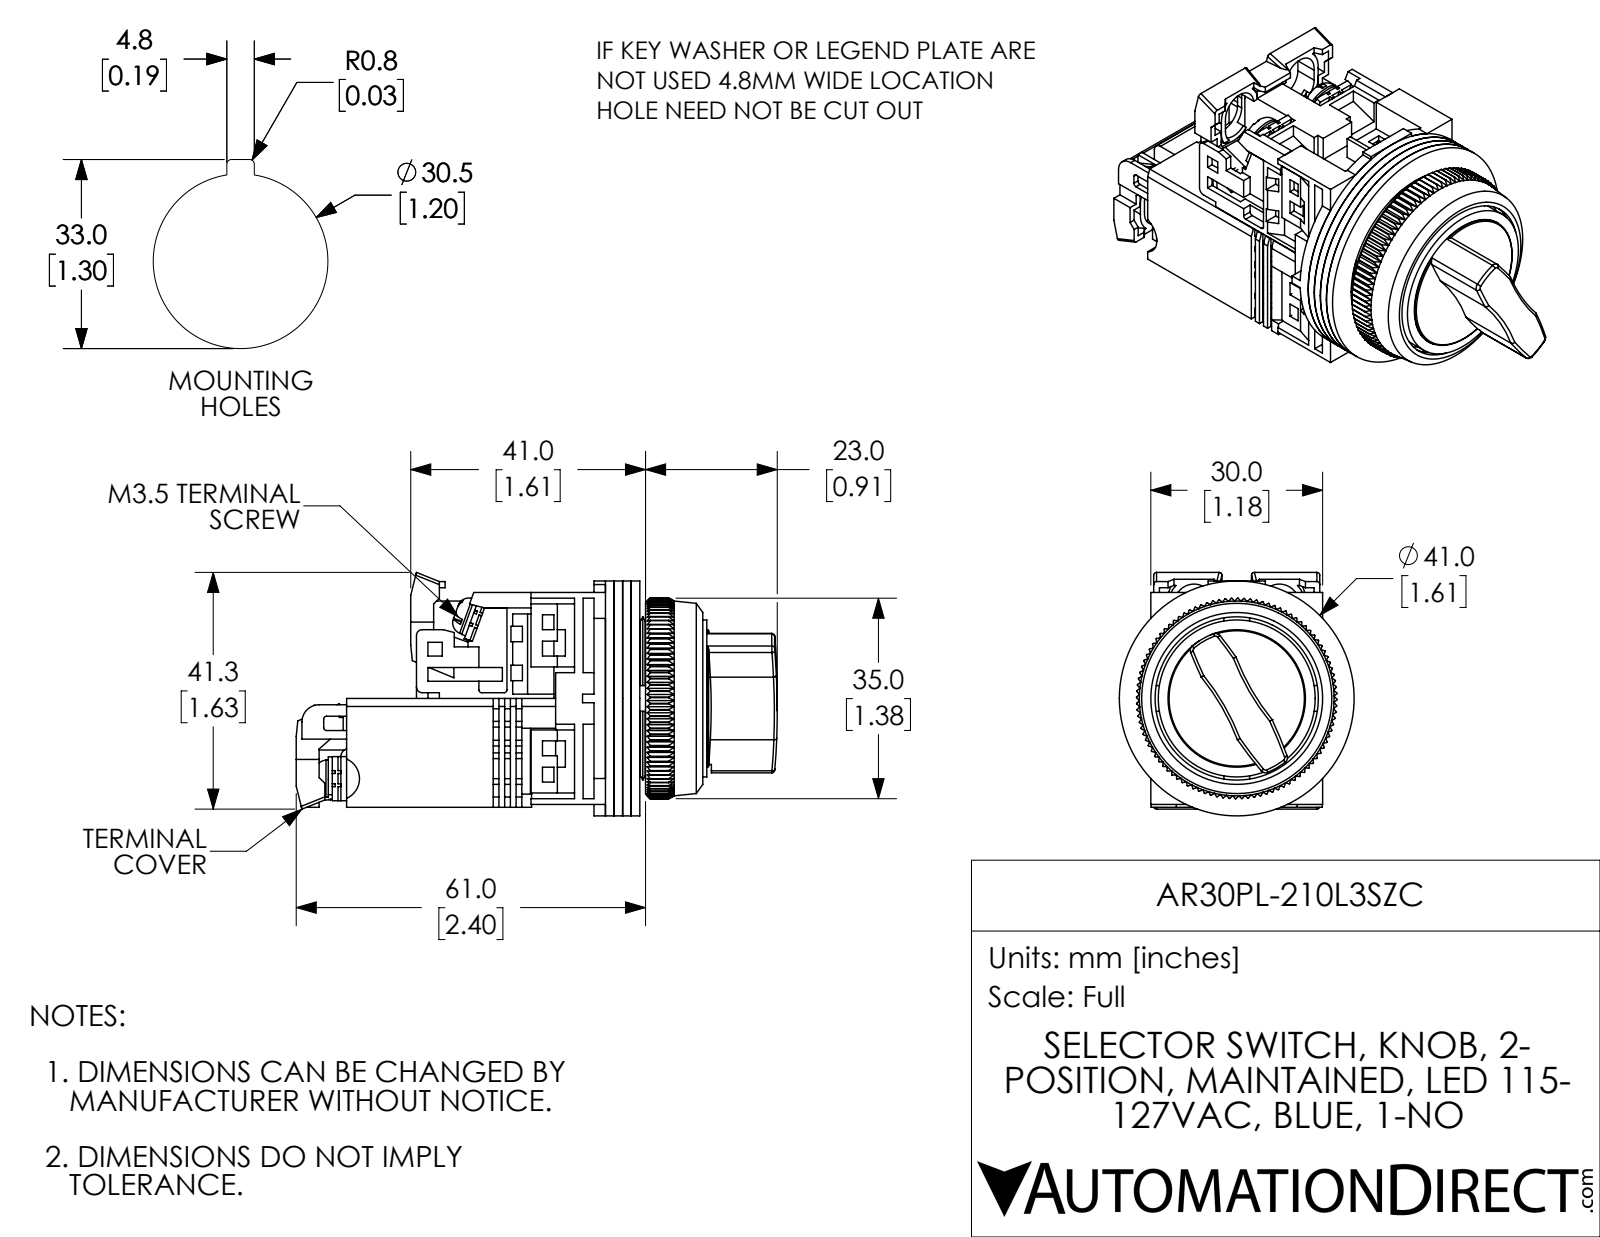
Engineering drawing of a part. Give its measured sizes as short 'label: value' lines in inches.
name: AR30PL-210L3SZC
written by: SolidWorks 2017 (AUTOMOTIVE_DESIGN)
unit: in
bodies: 27 solids, 2357 faces (1706 planar, 321 cylindrical, 330 other)
size: 3.307 × 1.673 × 1.614
volume: 3.001 in³; area: 63.38 in²
holes: 6× ⌀0.138, 4× ⌀0.142, 3× ⌀0.118, 1× ⌀0.472, 1× ⌀0.709, 1× ⌀0.768, 1× ⌀0.827, 1× ⌀1.122, 1× ⌀1.181, 1× ⌀1.252
bosses: 4× ⌀0.26, 2× ⌀0.138, 2× ⌀0.063, 1× ⌀1.614, 1× ⌀1.15, 1× ⌀1.079, 1× ⌀0.945, 1× ⌀0.886
rounds: 17× R0.059, 13× R0.02, 6× R0.039, 4× R0.138, 4× R0.177, 2× R0.118, 2× R1.575, 2× R2.953
face distances: 0.059, 0.118, 0.177, 0.079, 0.039, 0.748, 0.787, 0.197, 0.256, 1.417
hole spacings: 0.579, 0.297, 0.624, 0.02, 0.302, 0.583, 0.583, 0.606
